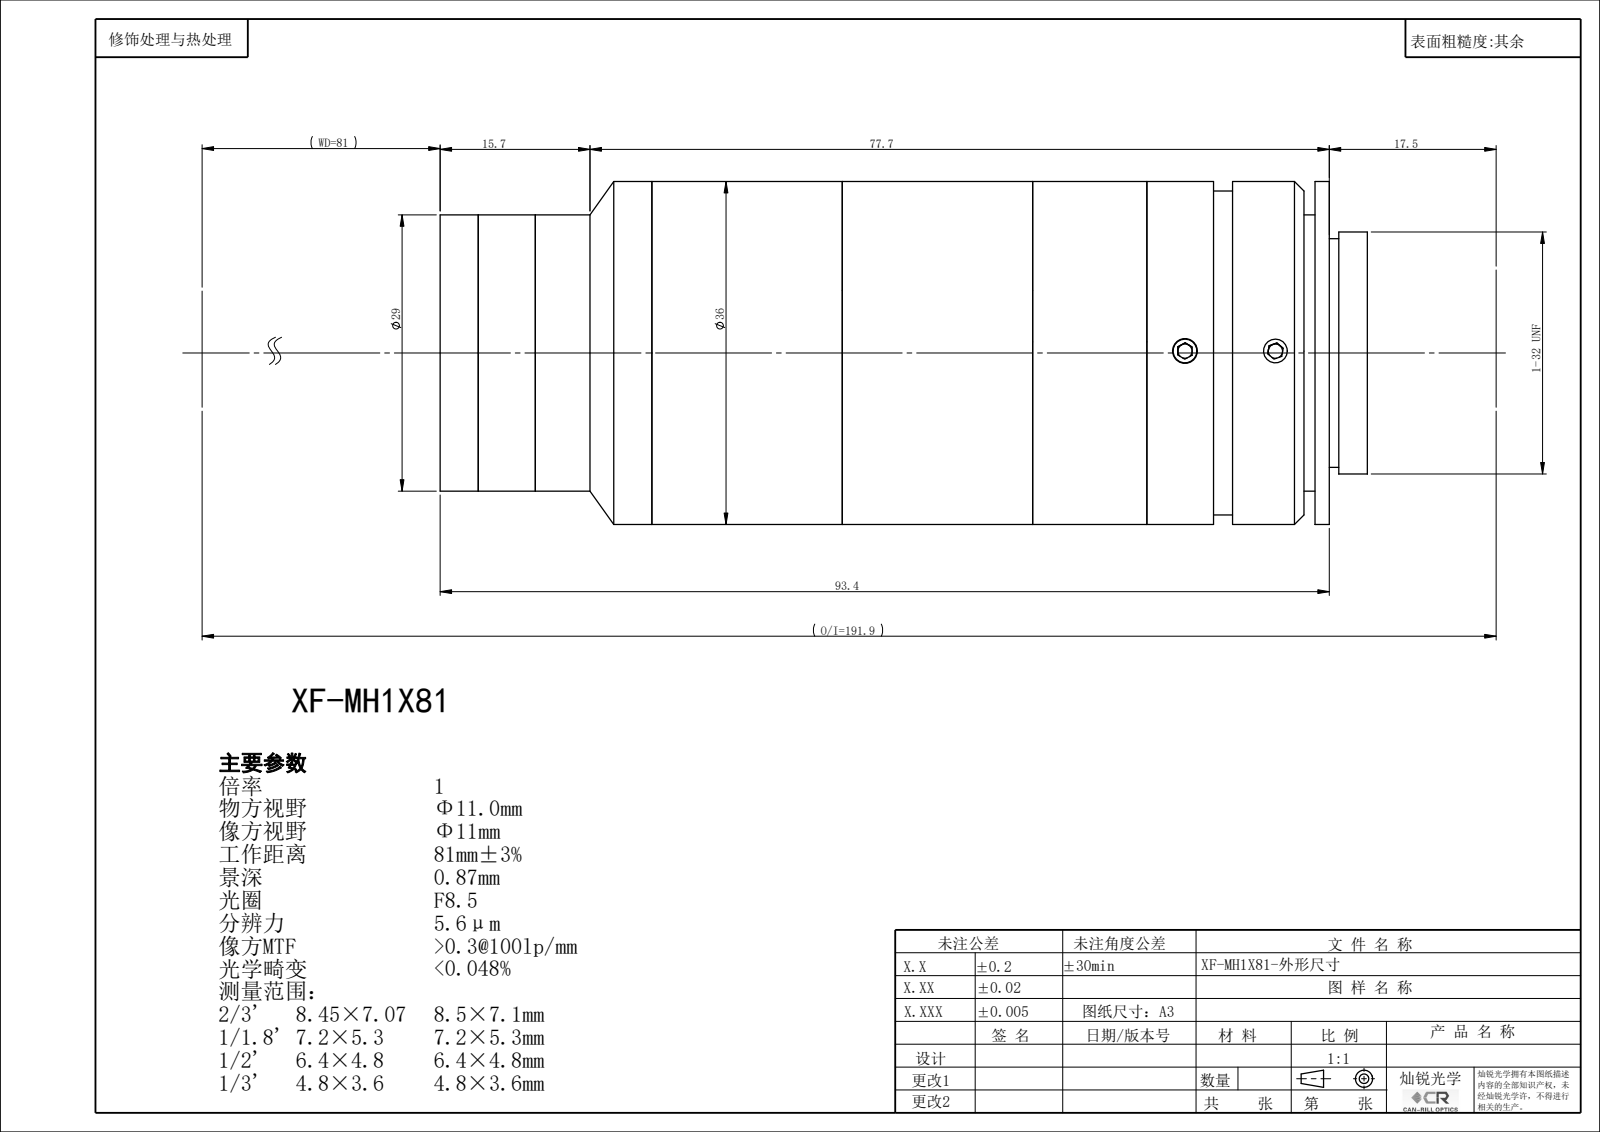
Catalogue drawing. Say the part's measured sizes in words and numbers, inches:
The part is named "XF-MH1X81". Its 3-D file was written by "SolidWorks 2022 (CONFIG_CONTROL_DESIGN)". It is 0 solids with 130 faces: 64 planar, 44 cylindrical and 22 other. Overall it measures 3.834 by 1.418 by 1.417 inches. Round holes: 3 of diameter 0.098, 1 of diameter 0.551, 1 of diameter 0.882, 1 of diameter 0.945, 1 of diameter 0.98, 1 of diameter 1.024, 1 of diameter 1.039. Round bosses or shafts: 1 of diameter 1.417, 1 of diameter 1.339, 1 of diameter 1.142, 1 of diameter 1. The main face-to-face distances are 0.754, 2.773, 3.527, 0.059, 3.468, 0.695, 2.301, 0.472, 1.167, 1.226.
